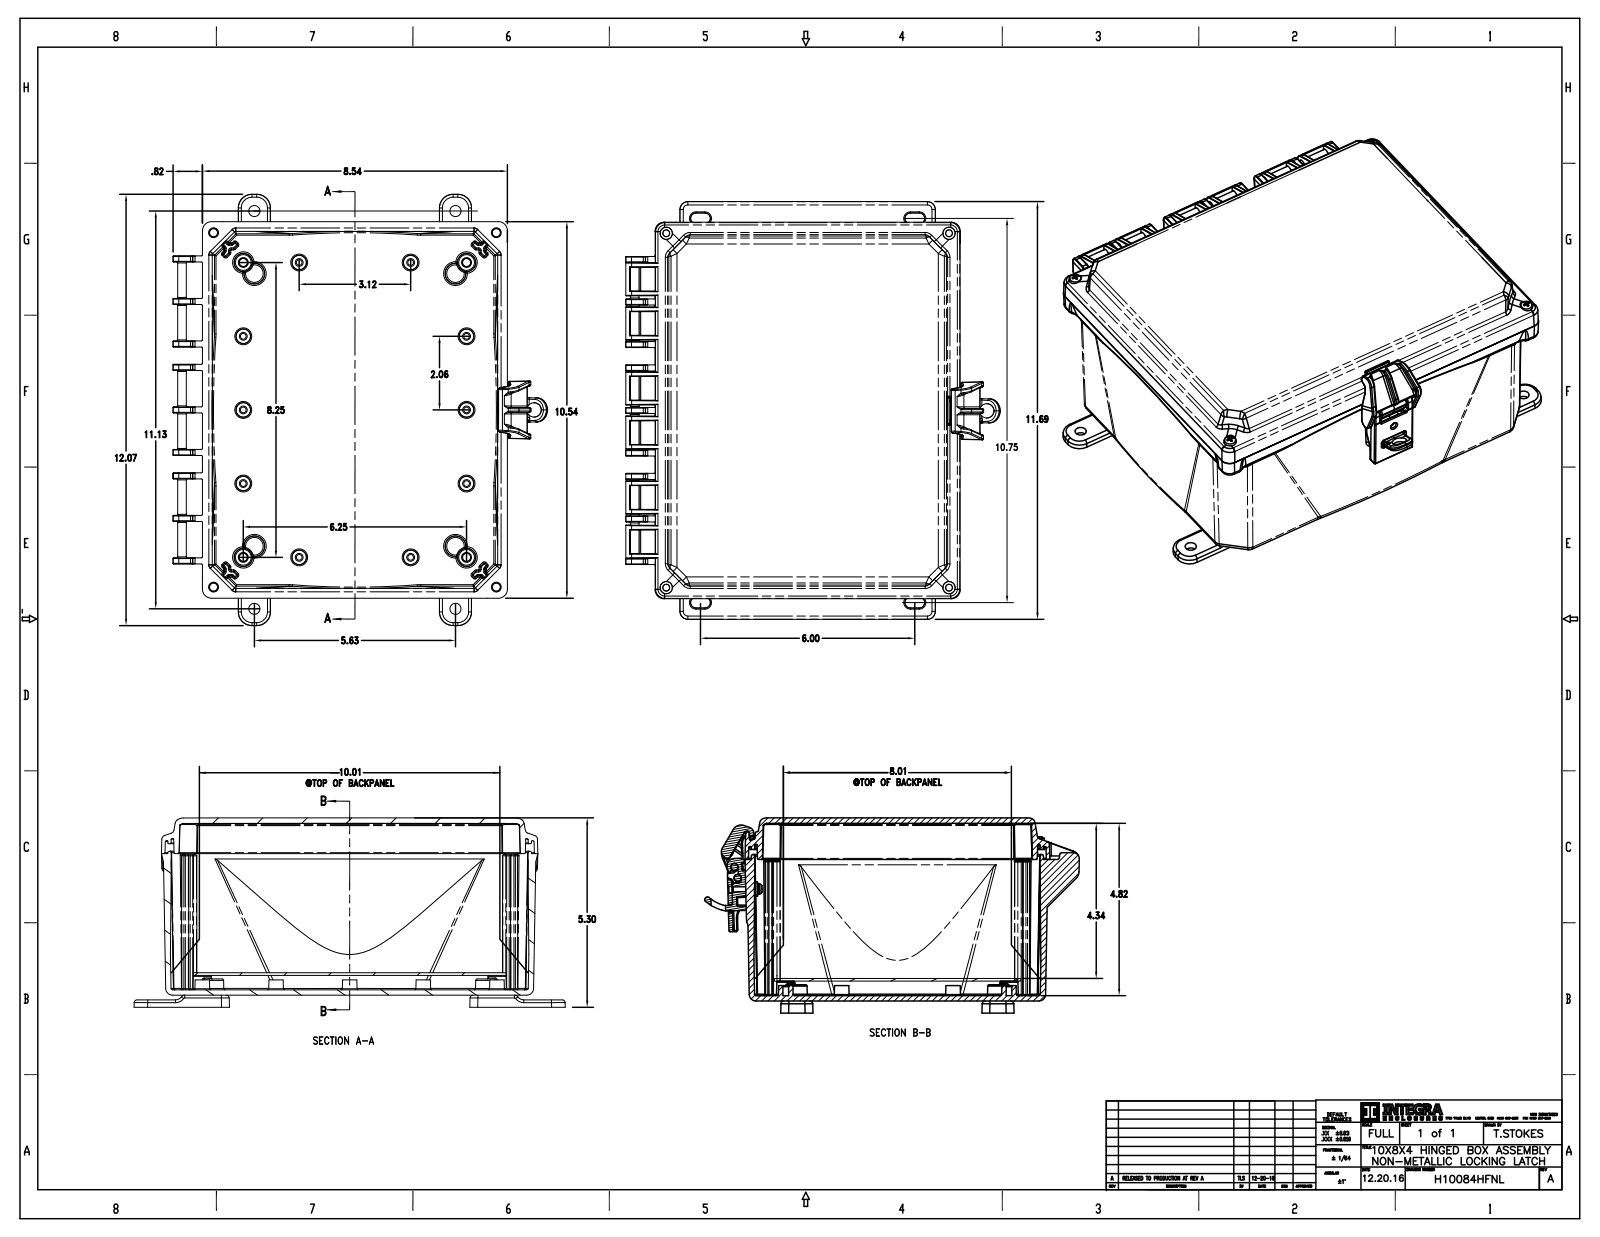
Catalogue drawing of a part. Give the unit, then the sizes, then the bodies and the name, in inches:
Units: inches
Overall size (bounding box): 11.69 × 10.487 × 5.465
Round holes (diameter × count): ⌀0.16 ×10, ⌀0.19 ×8, ⌀0.201 ×4, ⌀0.116 ×2, ⌀0.125 ×2, ⌀0.08 ×1, ⌀0.14 ×1, ⌀0.175 ×1, ⌀0.21 ×1, ⌀0.33 ×1, ⌀0.35 ×1, ⌀0.4 ×1
Round bosses / shafts (diameter × count): ⌀0.25 ×12, ⌀0.3 ×8, ⌀0.298 ×8, ⌀0.29 ×8, ⌀0.26 ×8, ⌀0.258 ×8, ⌀0.375 ×4, ⌀0.372 ×4
Partial cylindrical surfaces — rounded edges, fillets, slot ends (radius × count): R0.03 ×422, R0.02 ×179, R0.015 ×104, R0.005 ×49, R0.01 ×48, R0.04 ×42, R0.09 ×42, R0.1 ×28
Main face-to-face distances: 0.15, 0.49, 0.12, 3.81, 3.96, 0.392, 0.27, 4.08, 0.34, 0.098
Hole centre spacings: 9.916, 6.25, 0.275, 0.439, 1.178, 1.293, 1.565, 1.616
Volume: 67.15 in³ · Surface area: 934.4 in²
Bodies: 32 solids, 6790 faces (2766 planar, 2168 cylindrical, 1856 other)
Part name (STEP PRODUCT): H1084BH; 9912525-80-10; 9912521-80-10; H1084BH_ASM (+8 more)
STEP written by: CREO PARAMETRIC BY PTC INC, 2016050 (CONFIG_CONTROL_DESIGN)
